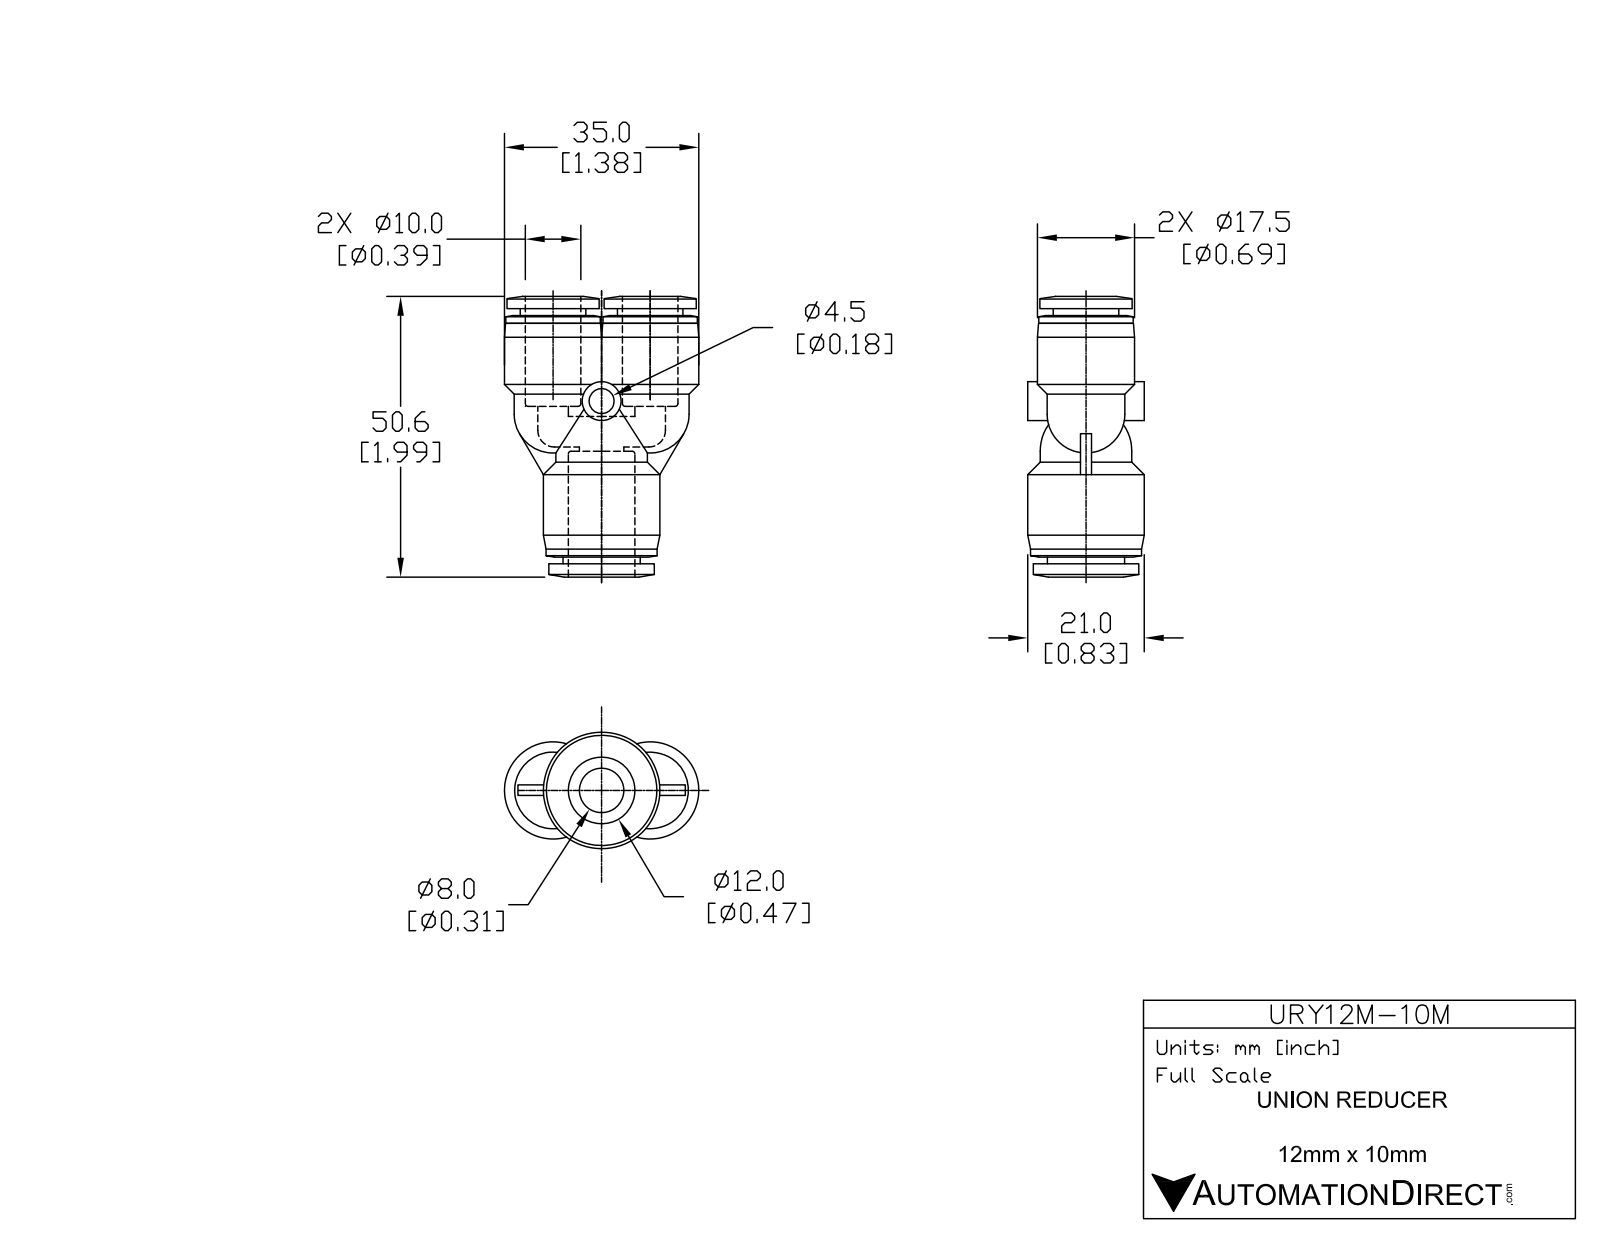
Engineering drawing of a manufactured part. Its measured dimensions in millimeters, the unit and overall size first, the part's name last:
Units: millimetres
Overall size (bounding box): 50.6 × 35 × 21
Round holes (diameter × count): ⌀10.3 ×2, ⌀4.5 ×1, ⌀12.3 ×1
Round bosses / shafts (diameter × count): ⌀17.5 ×2, ⌀17 ×2, ⌀16.6 ×2, ⌀14 ×2, ⌀11.8 ×2, ⌀21 ×1, ⌀20 ×1, ⌀19 ×1
Main face-to-face distances: 46.1, 44.8, 1.2, 28.3, 16.5, 17.7, 20.4, 8, 24.4, 25.7
Hole centre spacings: 8.7, 17.5
Volume: 11 800 mm³ · Surface area: 8 587 mm²
Bodies: 1 solid, 110 faces (20 planar, 44 cylindrical, 46 other)
Part name (STEP PRODUCT): URY12M-10M
STEP written by: SolidWorks 2015 (AUTOMOTIVE_DESIGN)
